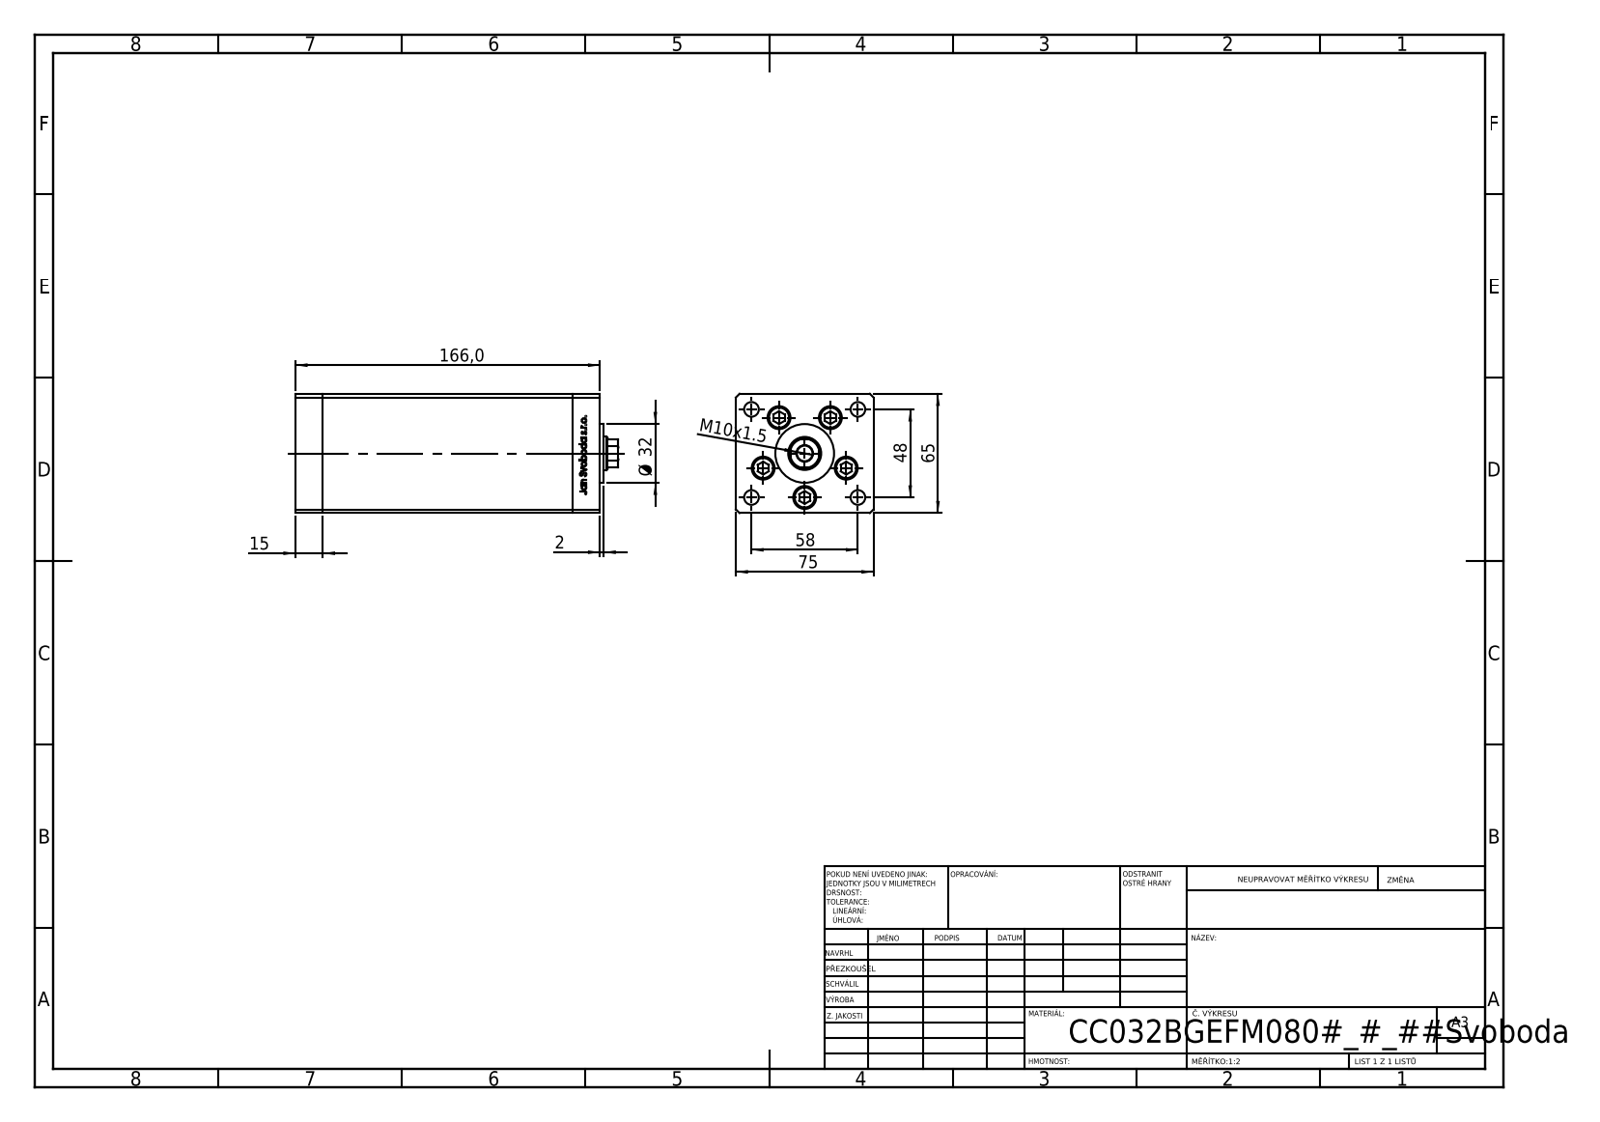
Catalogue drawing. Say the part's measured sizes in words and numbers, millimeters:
The part is named "V220C_B MIDDLE; V220C BACK_B; V220C_VC_B; V220C_FRONT_B (+1 more)". Its 3-D file was written by "SolidWorks 2019 (CONFIG_CONTROL_DESIGN)". It is 14 solids with 1183 faces: 462 planar, 147 cylindrical and 574 other. Overall it measures 176 by 75 by 65 millimeters. Its volume is 722 498 cubic millimeters and its surface area 127 363 square millimeters. Round holes: 5 of diameter 9, 5 of diameter 12.5, 4 of diameter 8, 2 of diameter 2, 2 of diameter 13.16, 1 of diameter 8.5, 1 of diameter 18. Round bosses or shafts: 5 of diameter 8, 1 of diameter 32. Partial cylindrical surfaces (rounded edges, fillets, slot ends): 2 of radius 0.93, 1 of radius 8.5. The main face-to-face distances are 75, 65, 15, 136, 151, 166, 28, 13, 54.5, 10.5. The hole center spacings are 24, 37.64, 15.67, 17.22, 27.71, 28.83, 29, 32.63.
